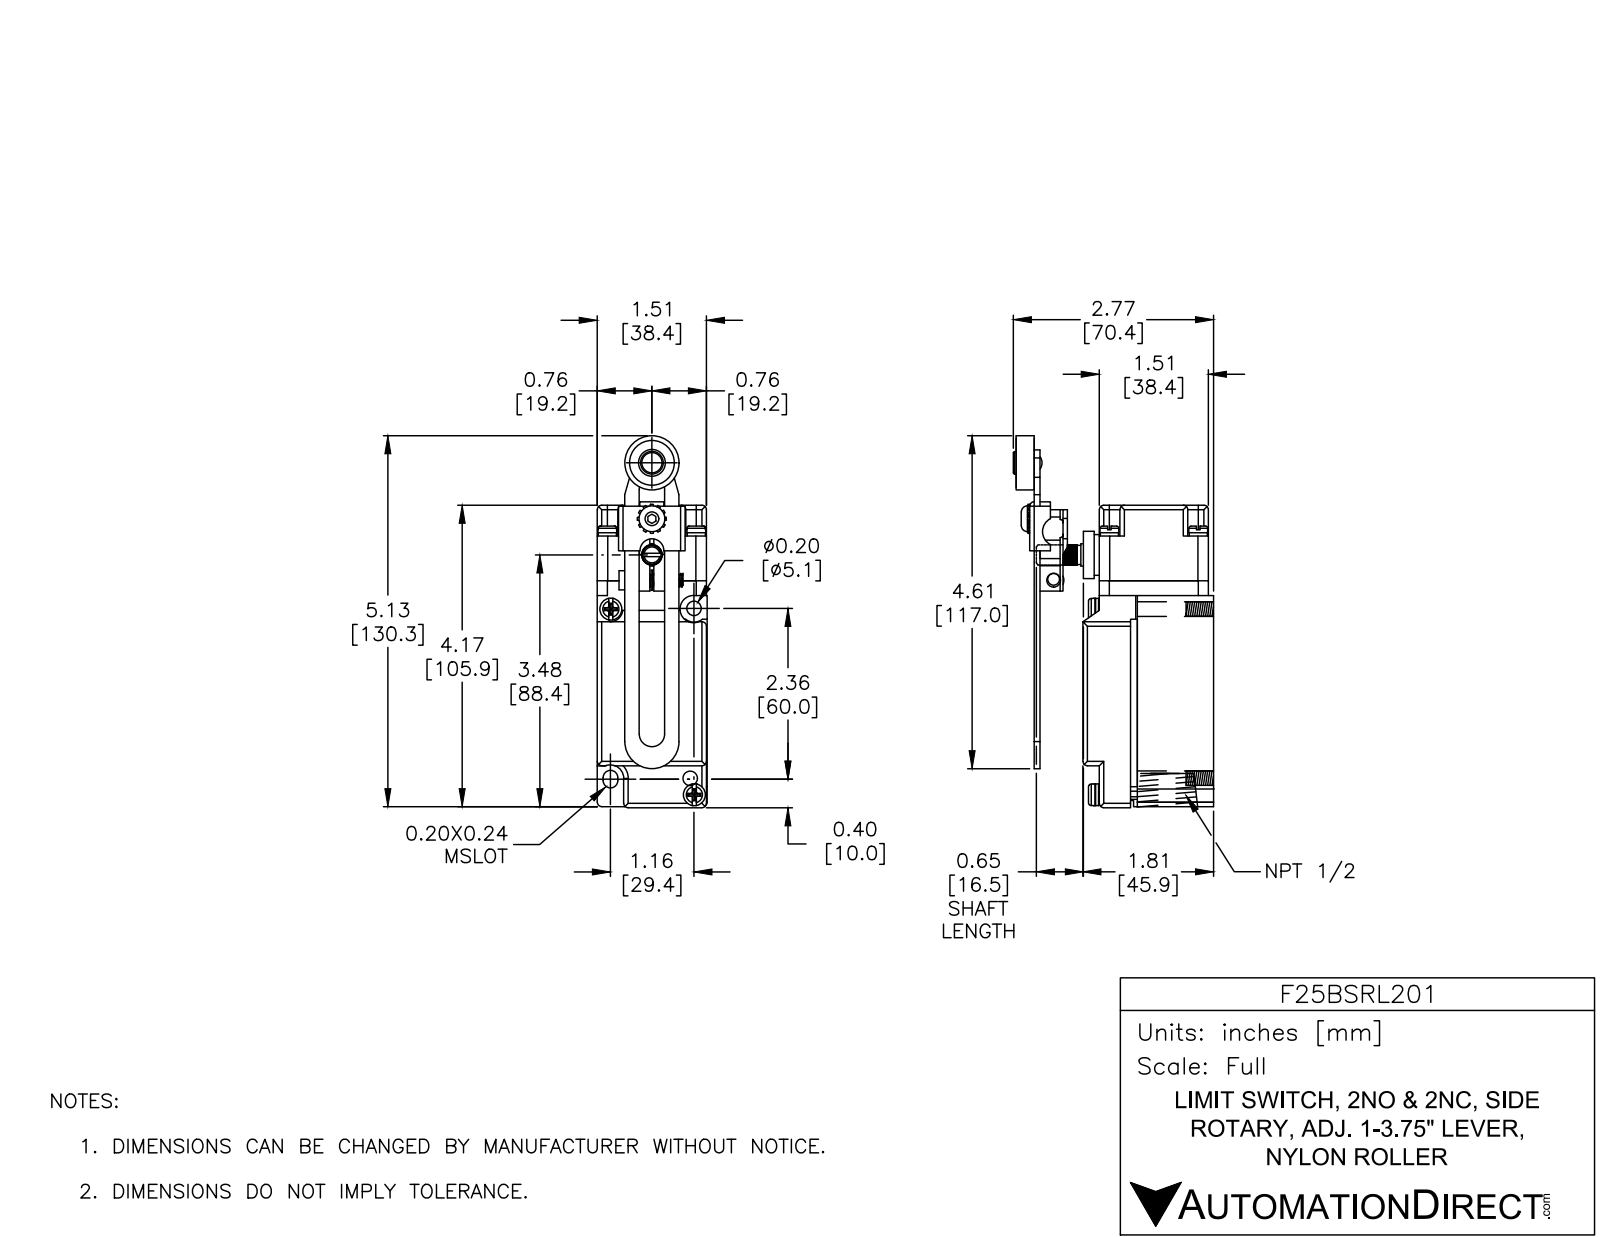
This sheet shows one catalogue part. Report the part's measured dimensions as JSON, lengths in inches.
{"part_name": "F25ASRL201; Imported76; Imported75; Imported80 (+8 more)", "step_written_by": "SolidWorks 2002296 (CONFIG_CONTROL_DESIGN)", "units": "inches", "bodies": {"solids": 21, "faces": 1109, "planar": 536, "cylindrical": 257, "other": 316}, "overall_size": [6.556, 2.866, 1.52], "volume_in3": 10.62, "surface_area_in2": 81.02, "round_holes": [[0.177, 4], [0.2, 4], [0.19, 3], [0.203, 2], [0.11, 1], [0.156, 1], [0.202, 1], [0.209, 1], [0.251, 1], [0.283, 1], [0.58, 1], [0.62, 1]], "round_bosses_or_shafts": [[0.26, 4], [0.25, 4], [0.302, 2], [0.3, 2], [0.75, 1], [0.655, 1], [0.565, 1], [0.375, 1]], "partial_cylinders_radius": [[0.062, 32], [0.03, 16], [0.015, 8], [0.145, 8], [0.14, 4], [0.04, 2], [0.1, 2], [0.102, 2]], "face_to_face_distances": [0.094, 1.149, 1.055, 1.52, 0.66, 0.754, 1.809, 1.51, 0.593, 0.674], "hole_center_spacings": [1.23, 1.23, 1.74, 2.815, 0.225, 0.23, 0.235, 0.27]}
